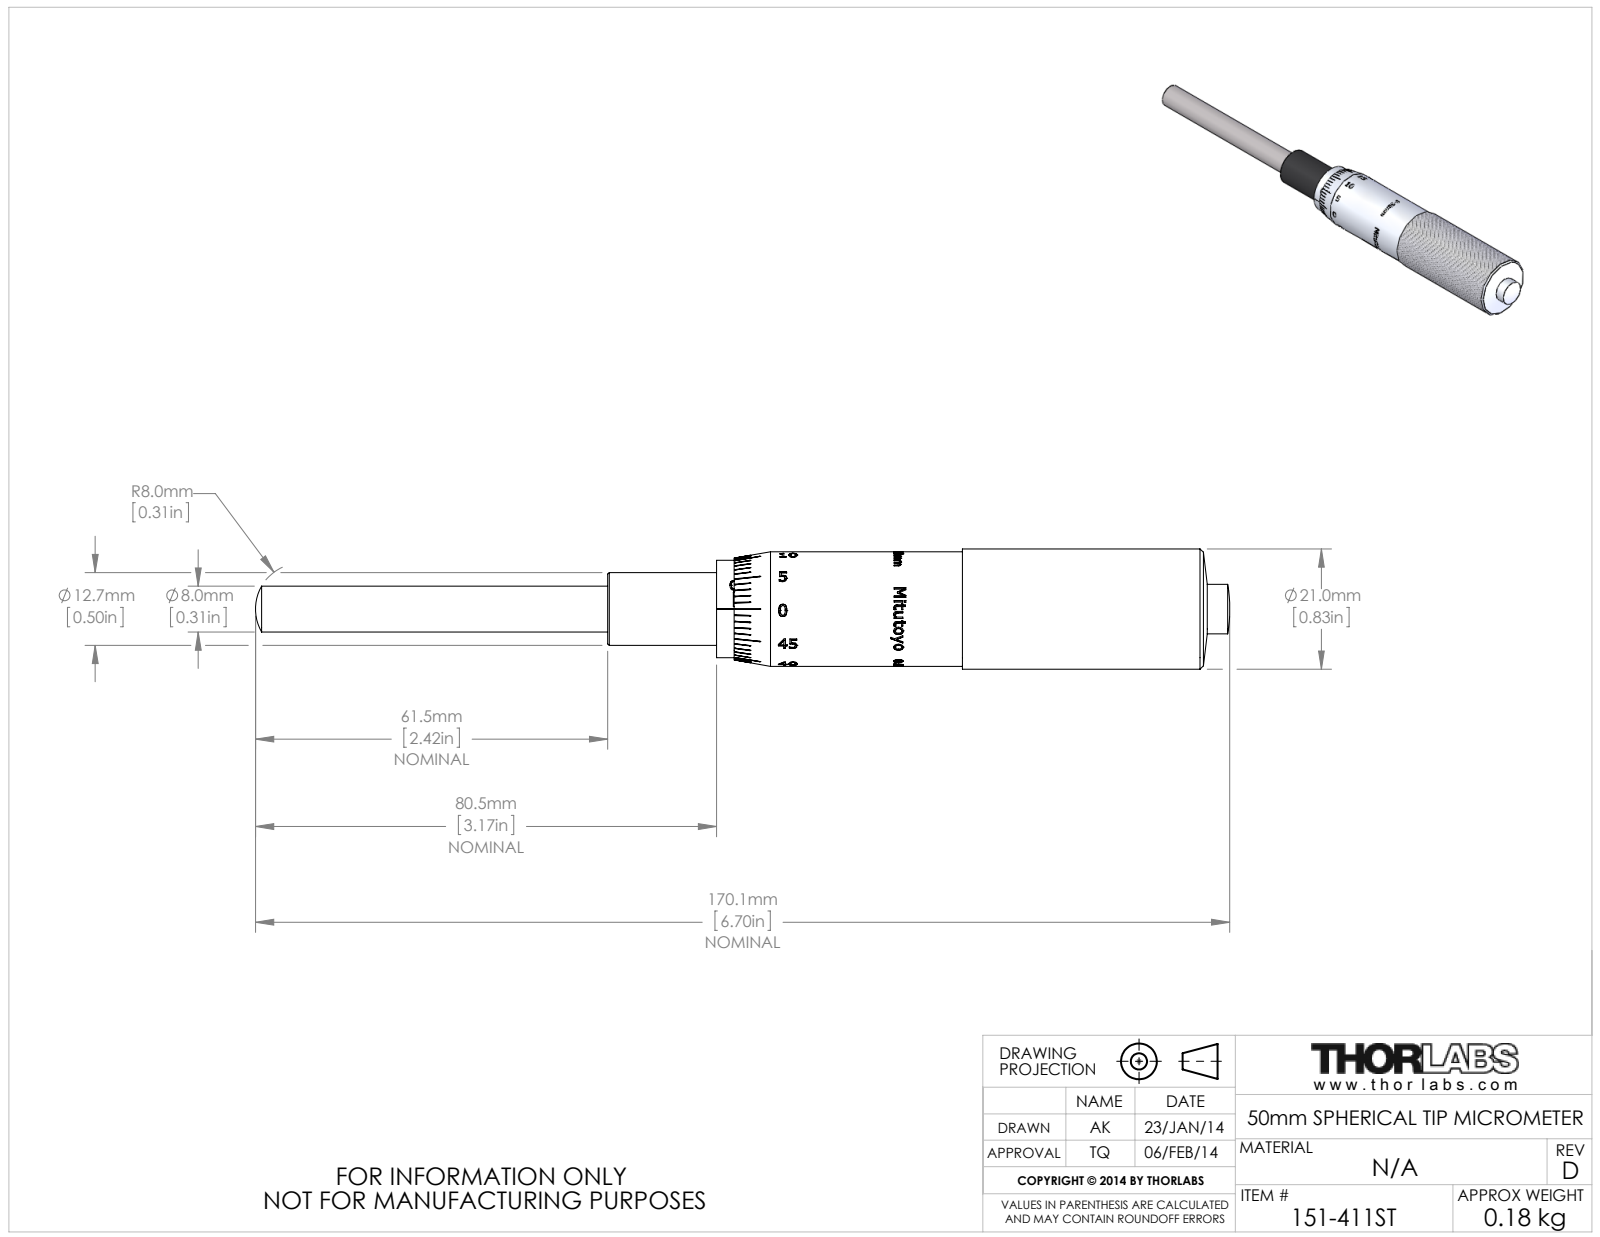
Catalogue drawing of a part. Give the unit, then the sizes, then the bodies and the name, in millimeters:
Units: millimetres
Overall size (bounding box): 170.1 × 21 × 21
Round holes (diameter × count): ⌀8 ×1, ⌀17.1 ×1
Round bosses / shafts (diameter × count): ⌀21 ×1, ⌀20 ×1, ⌀17 ×1, ⌀13.8 ×1, ⌀12.7 ×1, ⌀8.6 ×1
Partial cylindrical surfaces — rounded edges, fillets, slot ends (radius × count): R8.5 ×1, R8.9 ×1, R9.7 ×1, R10 ×1
Main face-to-face distances: 77.3, 68.5, 8.8, 19, 87.5, 96.3, 75, 56, 12.5, 21.3
Volume: 30 640 mm³ · Surface area: 20 740 mm²
Bodies: 2 solids, 1791 faces (966 planar, 227 cylindrical, 598 other)
Part name (STEP PRODUCT): 13435-E0W
STEP written by: SolidWorks 2012 (AUTOMOTIVE_DESIGN)
